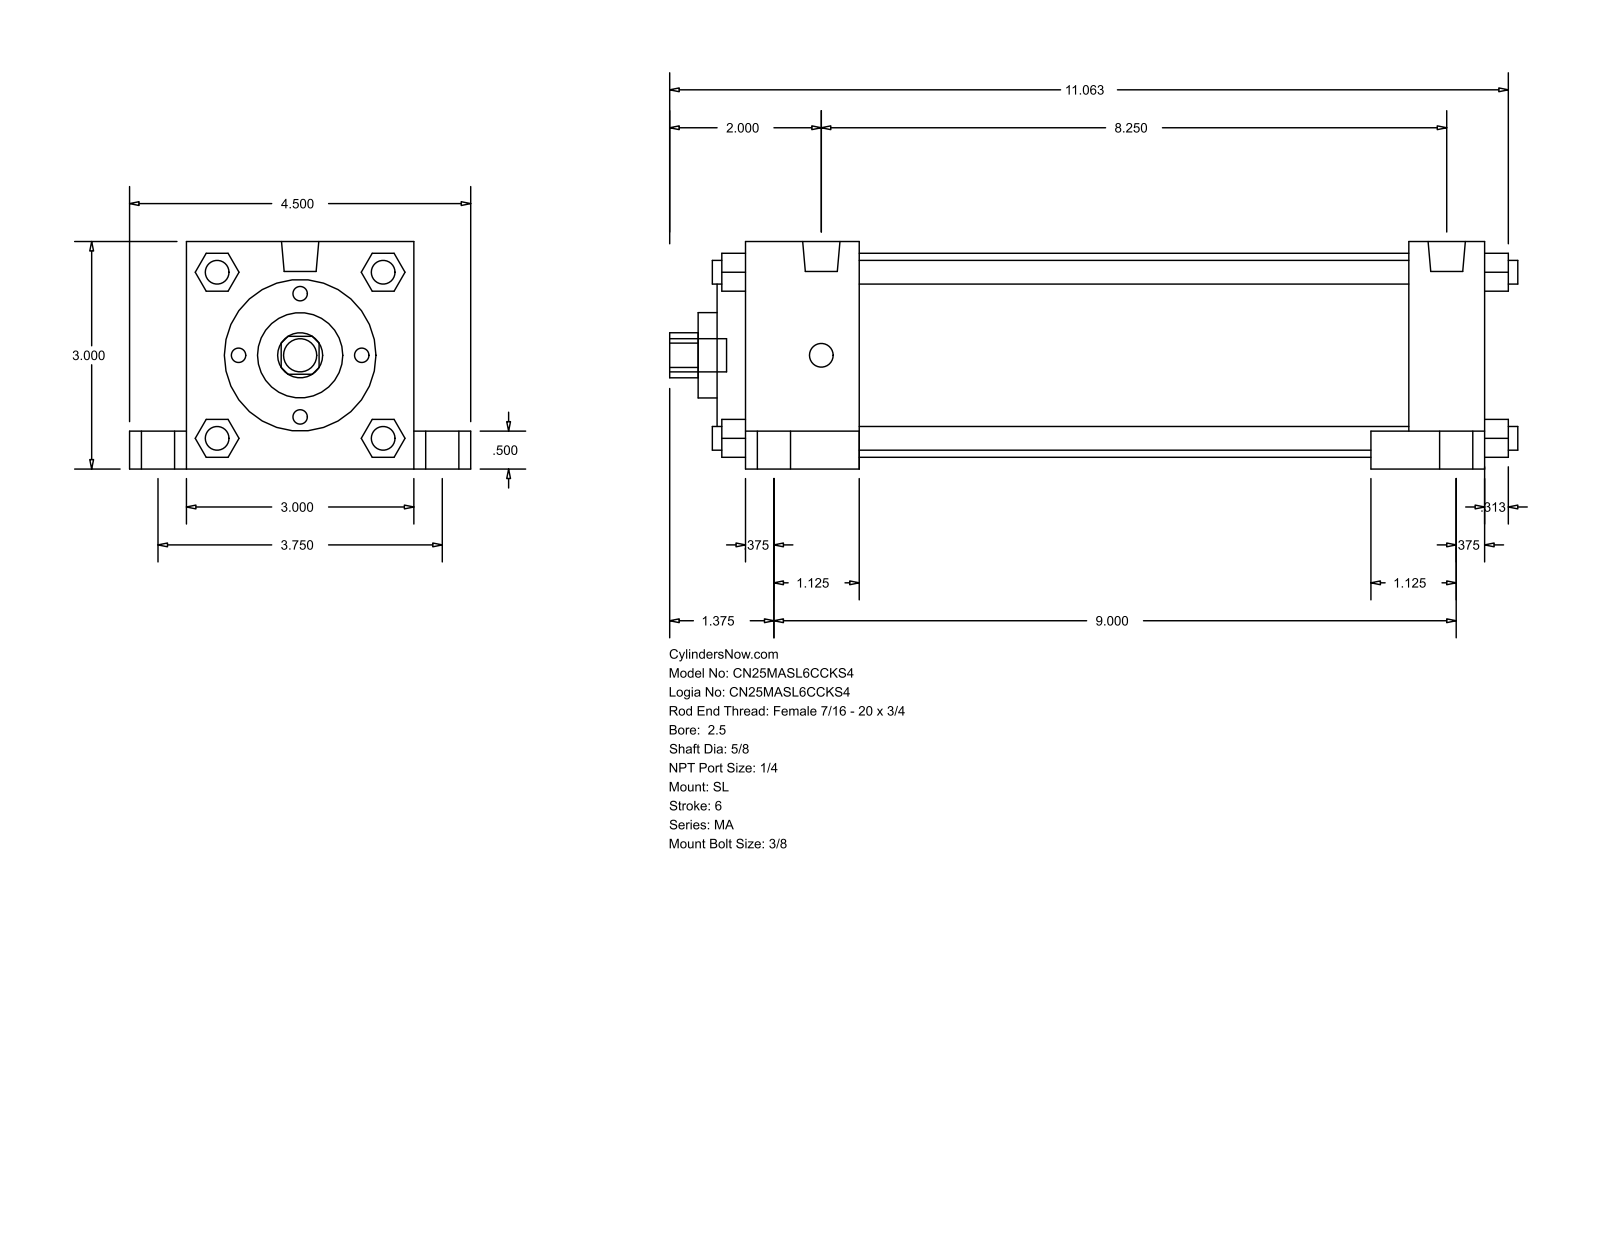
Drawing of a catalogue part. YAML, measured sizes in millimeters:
part_name: "MA_SL__0250_0.625"
step_written_by: "GSSL Pune (CONFIG_CONTROL_DESIGN)"
units: millimeters
bodies: {solids: 0, faces: 150, planar: 113, cylindrical: 37, other: 0}
overall_size: [284.16, 114.3, 76.2]
round_holes:
  - {diameter: 15.88, count: 1}
  - {diameter: 28.57, count: 1}
  - {diameter: 50.8, count: 1}
  - {diameter: 68.33, count: 1}
round_bosses_or_shafts:
  - {diameter: 7.94, count: 8}
  - {diameter: 11.11, count: 5}
  - {diameter: 17.46, count: 4}
  - {diameter: 12.49, count: 2}
partial_cylinders:
  - {radius: 7.54, count: 1}
face_to_face_distances: [76.2, 247.65, 12.7, 184.15, 25.4, 38.1, 209.55, 222.25, 19.05, 63.5]
